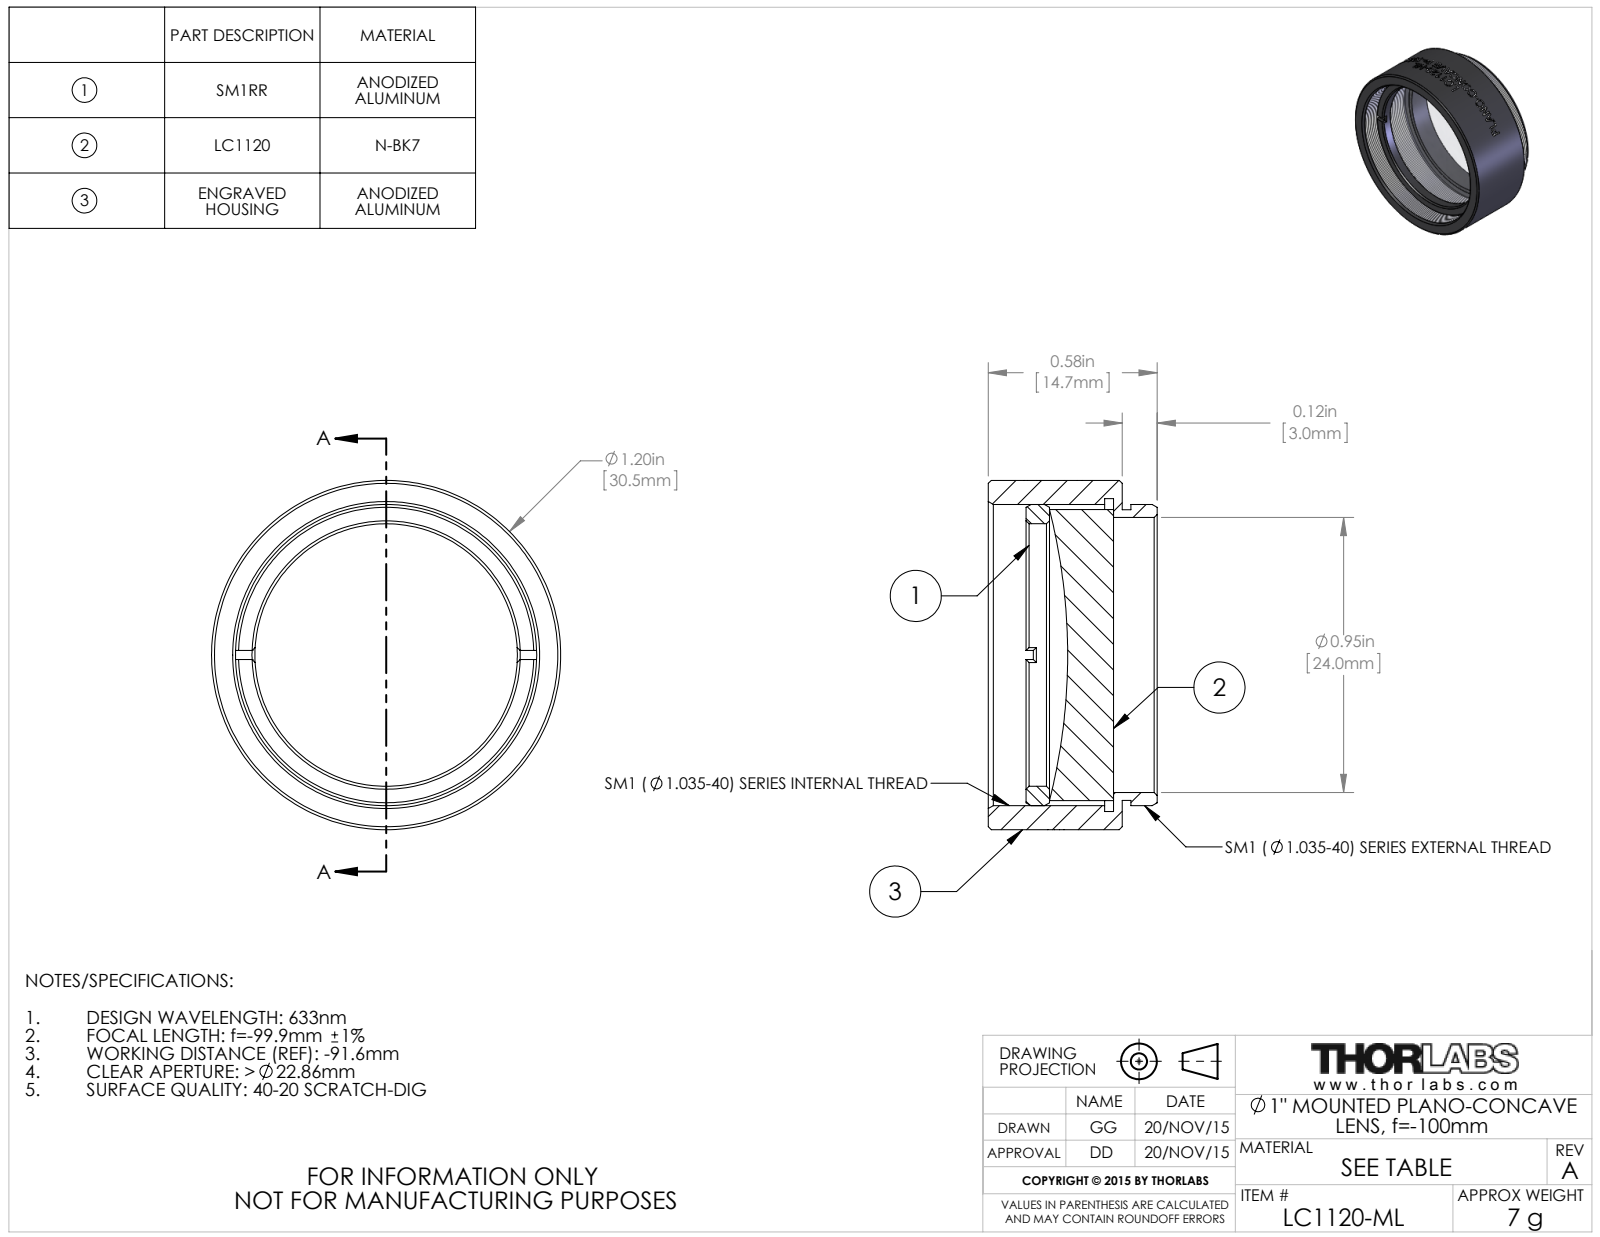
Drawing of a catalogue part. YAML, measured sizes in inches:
part_name: "TTN045310-E0W"
step_written_by: "SolidWorks 2014 (CONFIG_CONTROL_DESIGN)"
units: inches
bodies: {solids: 3, faces: 118, planar: 20, cylindrical: 74, other: 24}
overall_size: [1.2, 1.2, 0.58]
volume: 0.313
surface_area: 8.054
round_holes:
  - {diameter: 0.902, count: 1}
  - {diameter: 0.945, count: 1}
  - {diameter: 1.075, count: 1}
round_bosses_or_shafts:
  - {diameter: 1.2, count: 1}
  - {diameter: 1.035, count: 1}
  - {diameter: 1, count: 1}
  - {diameter: 0.999, count: 1}
face_to_face_distances: [0.03, 0.46, 0.43, 0.25, 0.22, 0.21, 0.33, 0.3, 0.08, 0.13]
